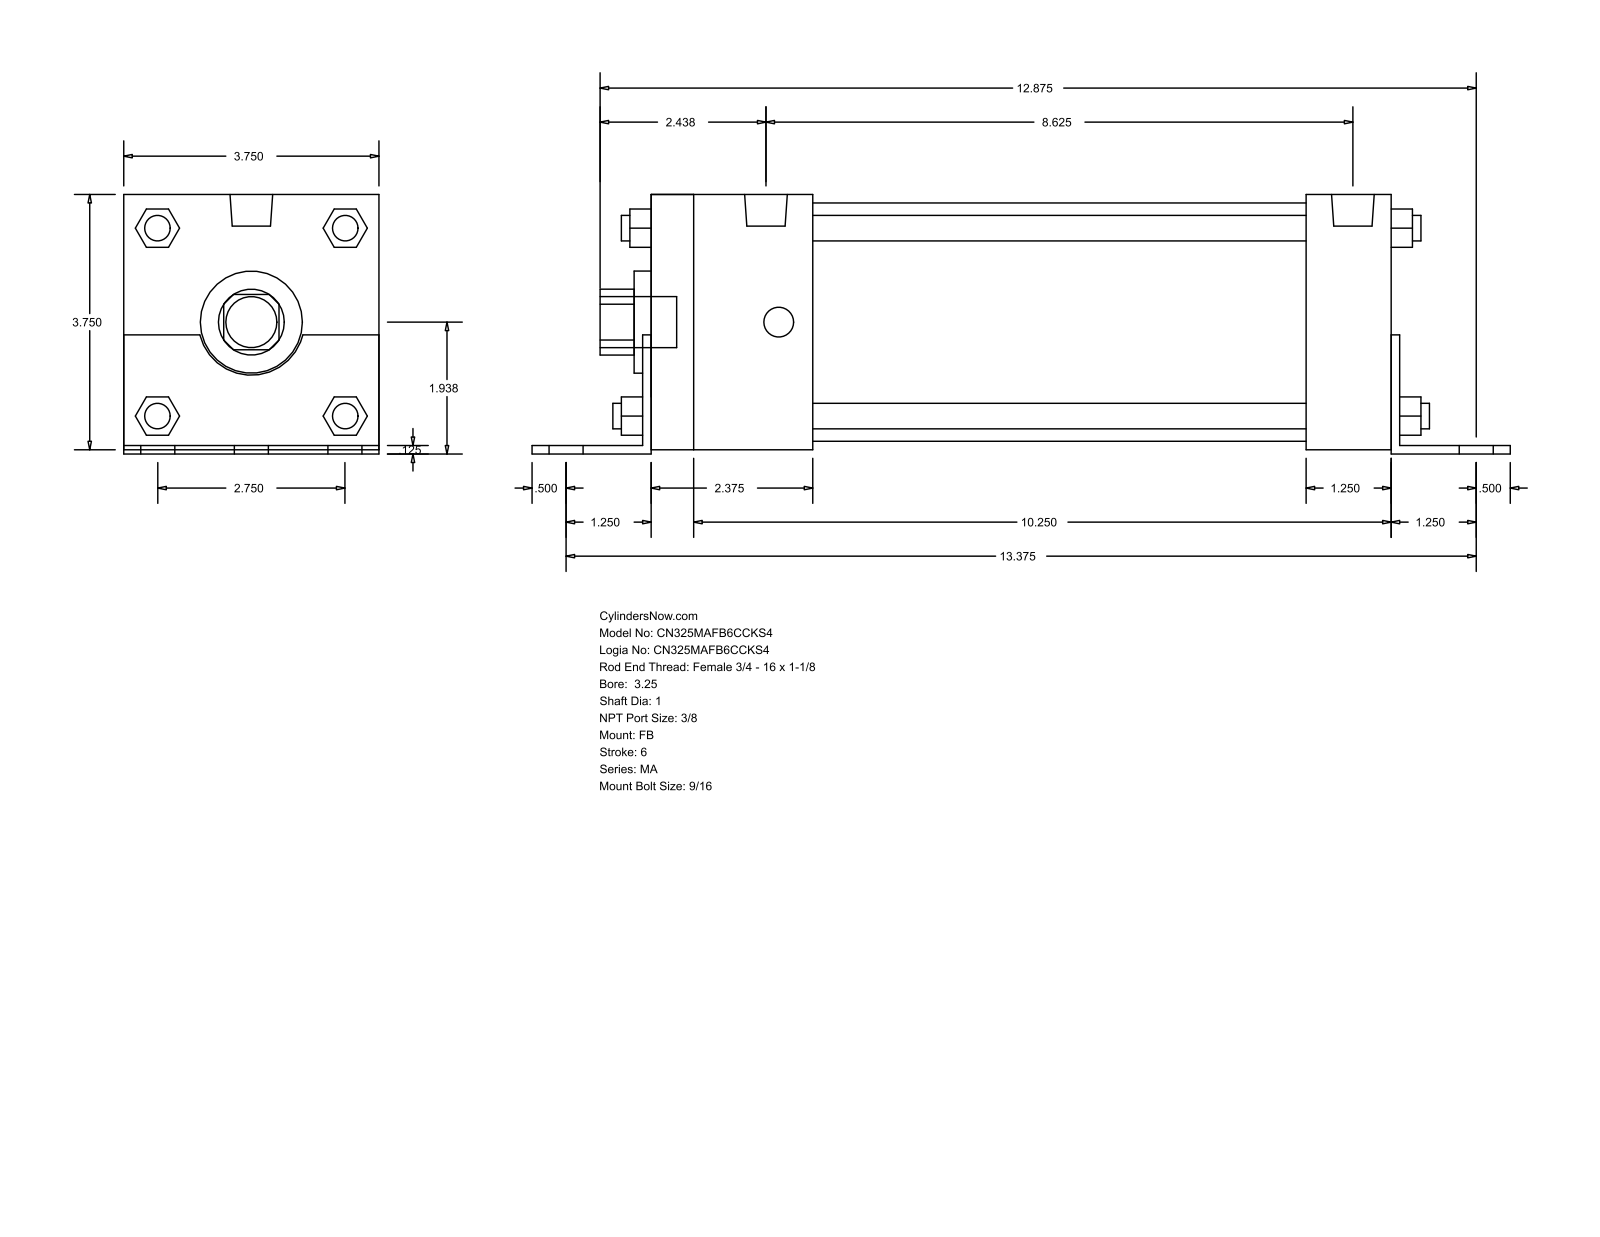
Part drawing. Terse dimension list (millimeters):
name: MA_FB__0325_1
written by: GSSL Pune (CONFIG_CONTROL_DESIGN)
unit: mm
bodies: 0 solids, 140 faces (105 planar, 35 cylindrical, 0 other)
size: 365.12 × 96.84 × 95.25
holes: 1× ⌀25.4, 1× ⌀38.1, 1× ⌀88.9
bosses: 6× ⌀14.29, 4× ⌀11.11, 4× ⌀9.53, 2× ⌀15.93, 1× ⌀19.05
rounds: 1× R12.29, 1× R19.81
face distances: 95.24, 3.17, 1.59, 96.83, 1.58, 93.66, 3.18, 276.22, 282.57, 279.4
